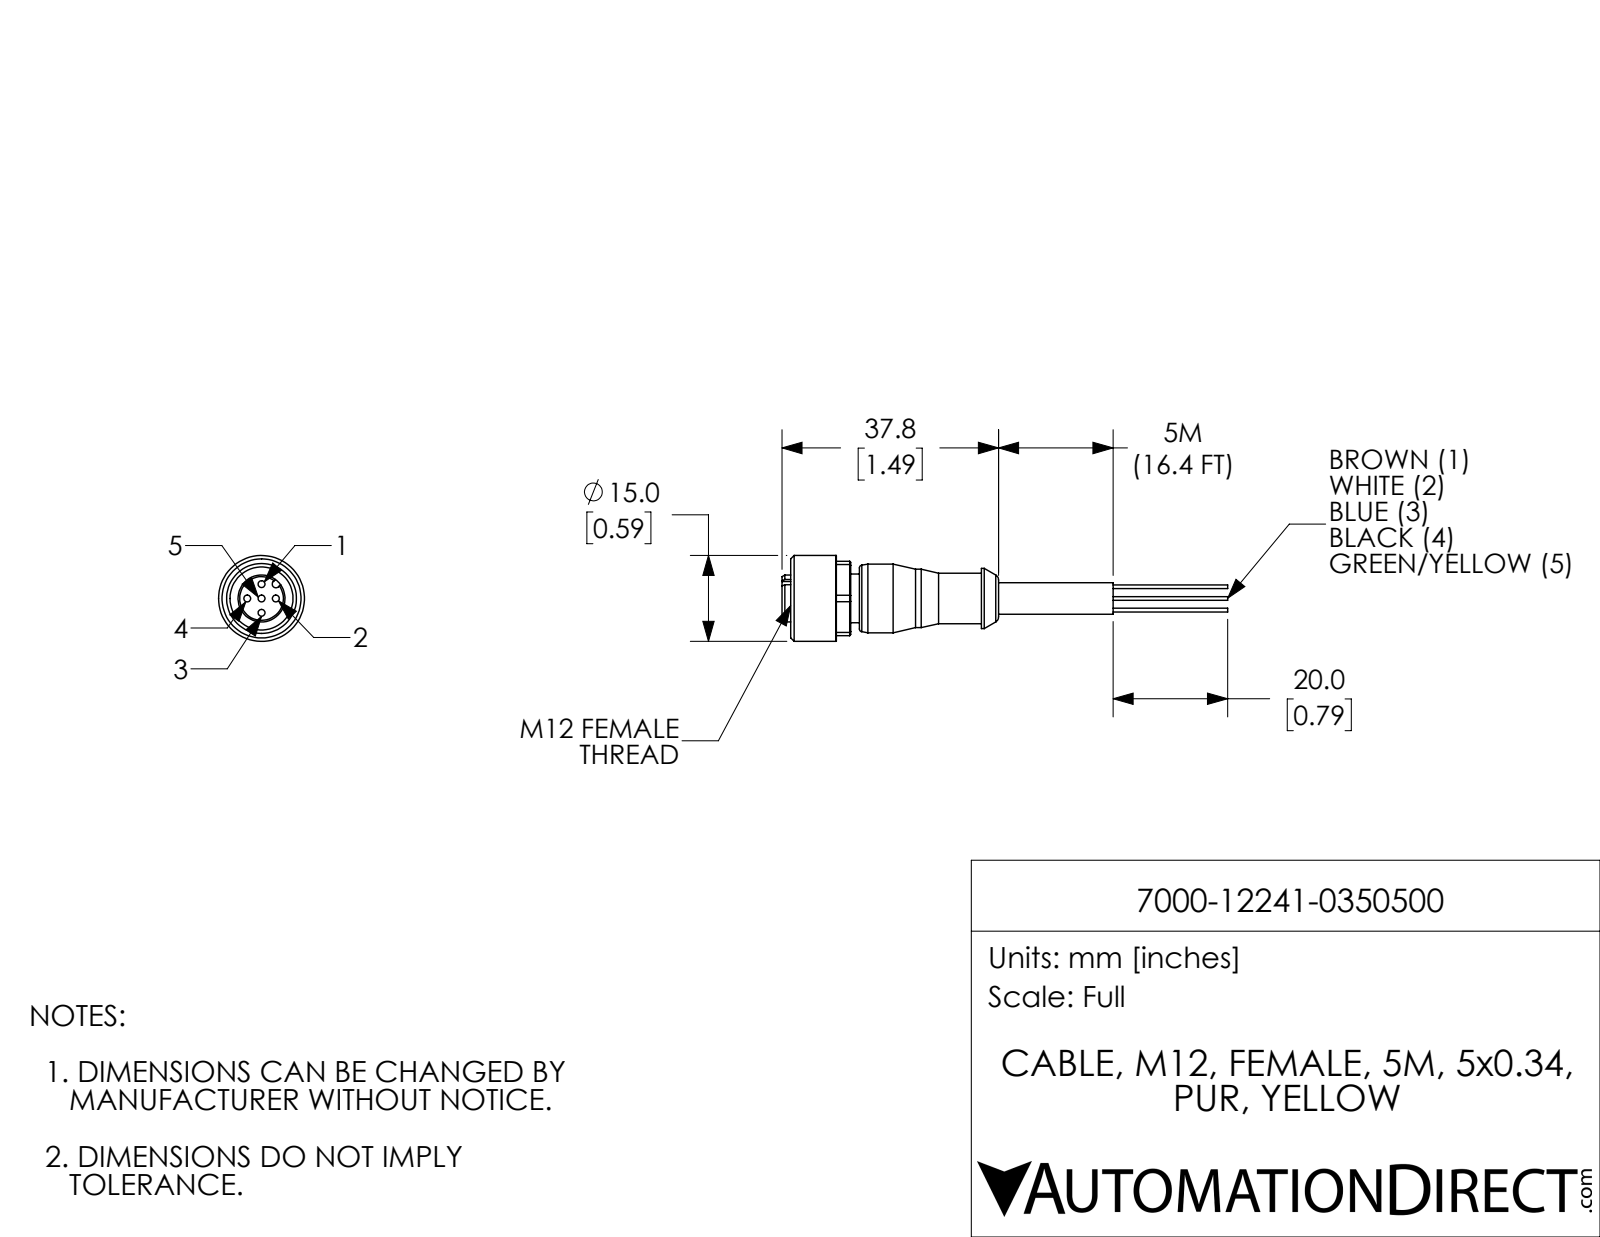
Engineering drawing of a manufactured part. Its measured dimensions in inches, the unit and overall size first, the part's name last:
Units: inches
Overall size (bounding box): 3.063 × 0.591 × 0.591
Round holes (diameter × count): ⌀0.047 ×5, ⌀0.433 ×1
Round bosses / shafts (diameter × count): ⌀0.026 ×5, ⌀0.591 ×1, ⌀0.472 ×1, ⌀0.413 ×1, ⌀0.402 ×1, ⌀0.346 ×1, ⌀0.335 ×1, ⌀0.323 ×1
Partial cylindrical surfaces — rounded edges, fillets, slot ends (radius × count): R0.026 ×1, R0.283 ×1
Main face-to-face distances: 0.472, 0.059, 0.118, 0.512, 0.354, 1.016, 0.295, 0.413, 0.098, 0.531
Hole centre spacings: 0.098, 0.139, 0.197
Volume: 0.248 in³ · Surface area: 4.45 in²
Bodies: 1 solid, 106 faces (34 planar, 45 cylindrical, 27 other)
Part name (STEP PRODUCT): 7000-12241-0350500
STEP written by: SolidWorks 2021 (CONFIG_CONTROL_DESIGN)
